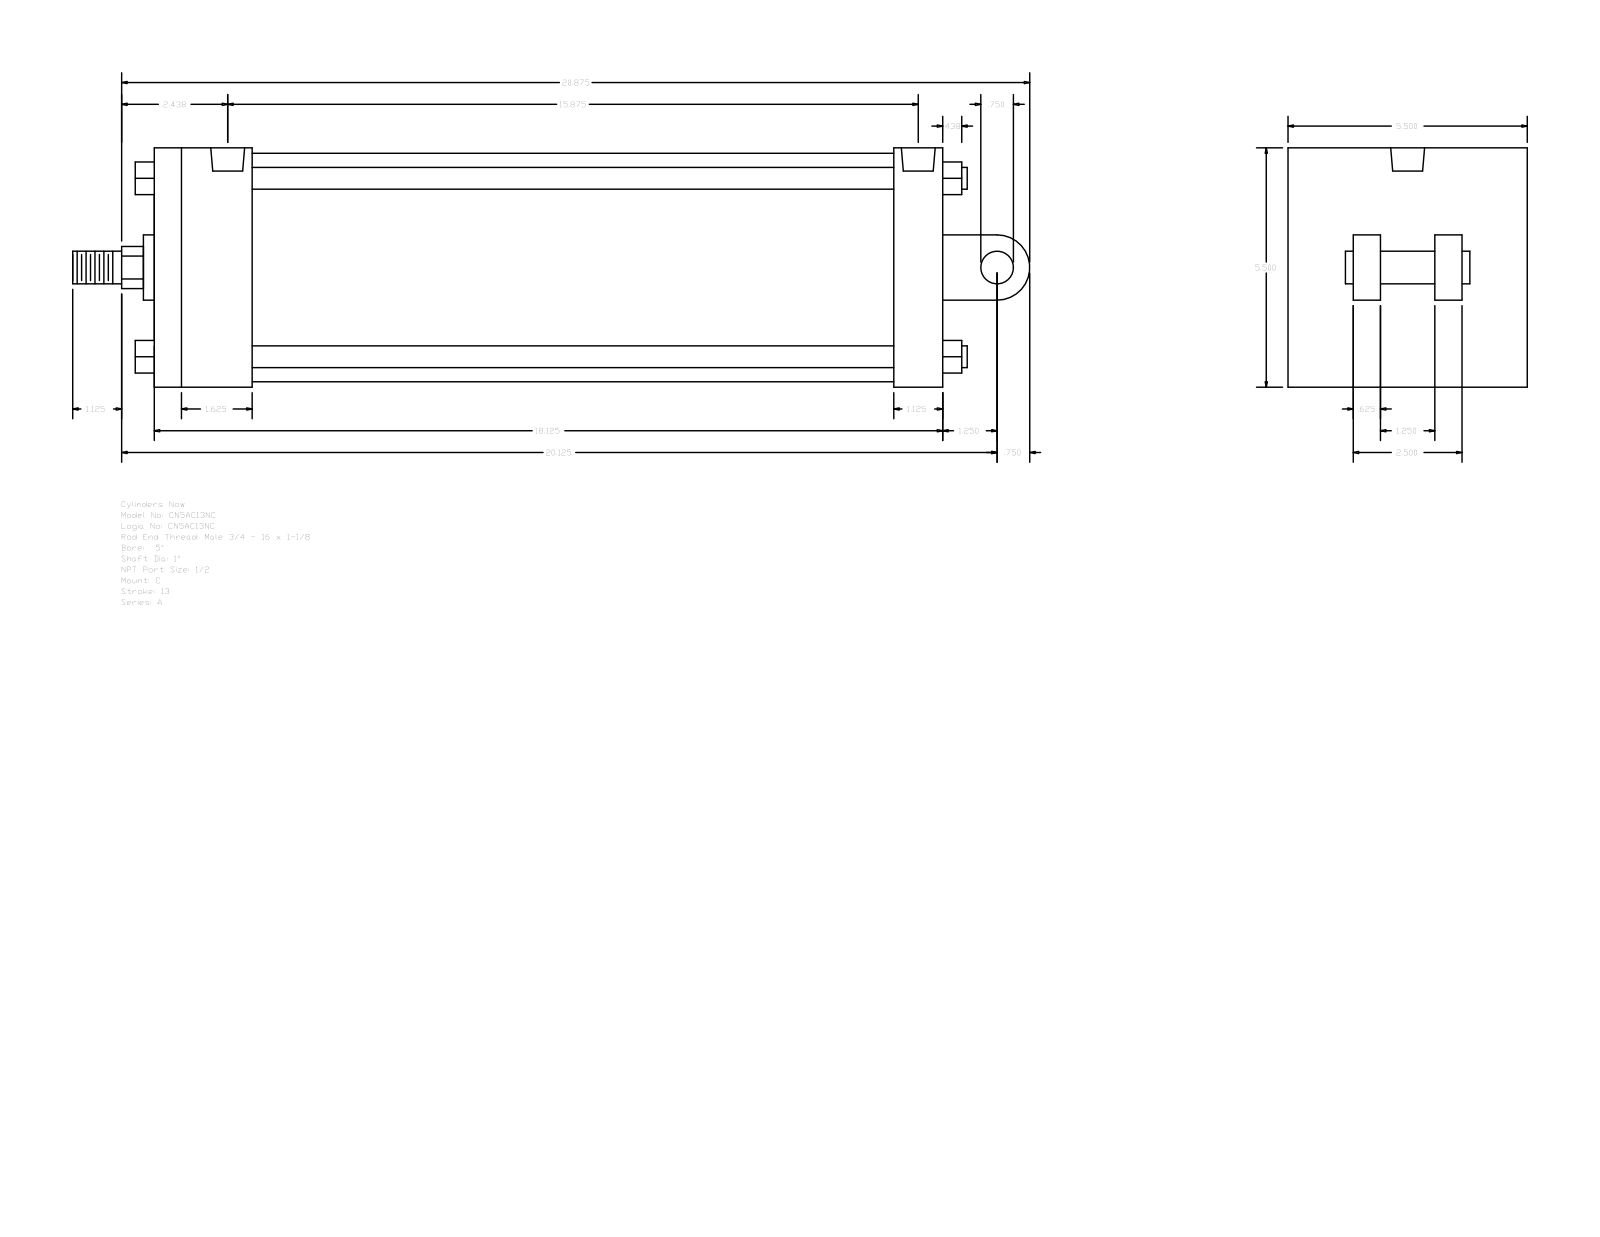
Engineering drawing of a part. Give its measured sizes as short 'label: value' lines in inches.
name: A_C__0500_1
written by: GSSL Pune (CONFIG_CONTROL_DESIGN)
unit: in
bodies: 0 solids, 135 faces (102 planar, 33 cylindrical, 0 other)
size: 22 × 5.5 × 5.5
holes: 4× ⌀0.344, 2× ⌀0.778
bosses: 4× ⌀0.5, 2× ⌀0.75, 1× ⌀5.25, 1× ⌀1.5, 1× ⌀1
rounds: 1× R0.484, 1× R0.75
face distances: 5.5, 18.125, 2.25, 17, 14.75, 15.875, 1.125, 1.5, 4, 2.125
hole spacings: 0.094, 15.687, 15.781, 15.875
